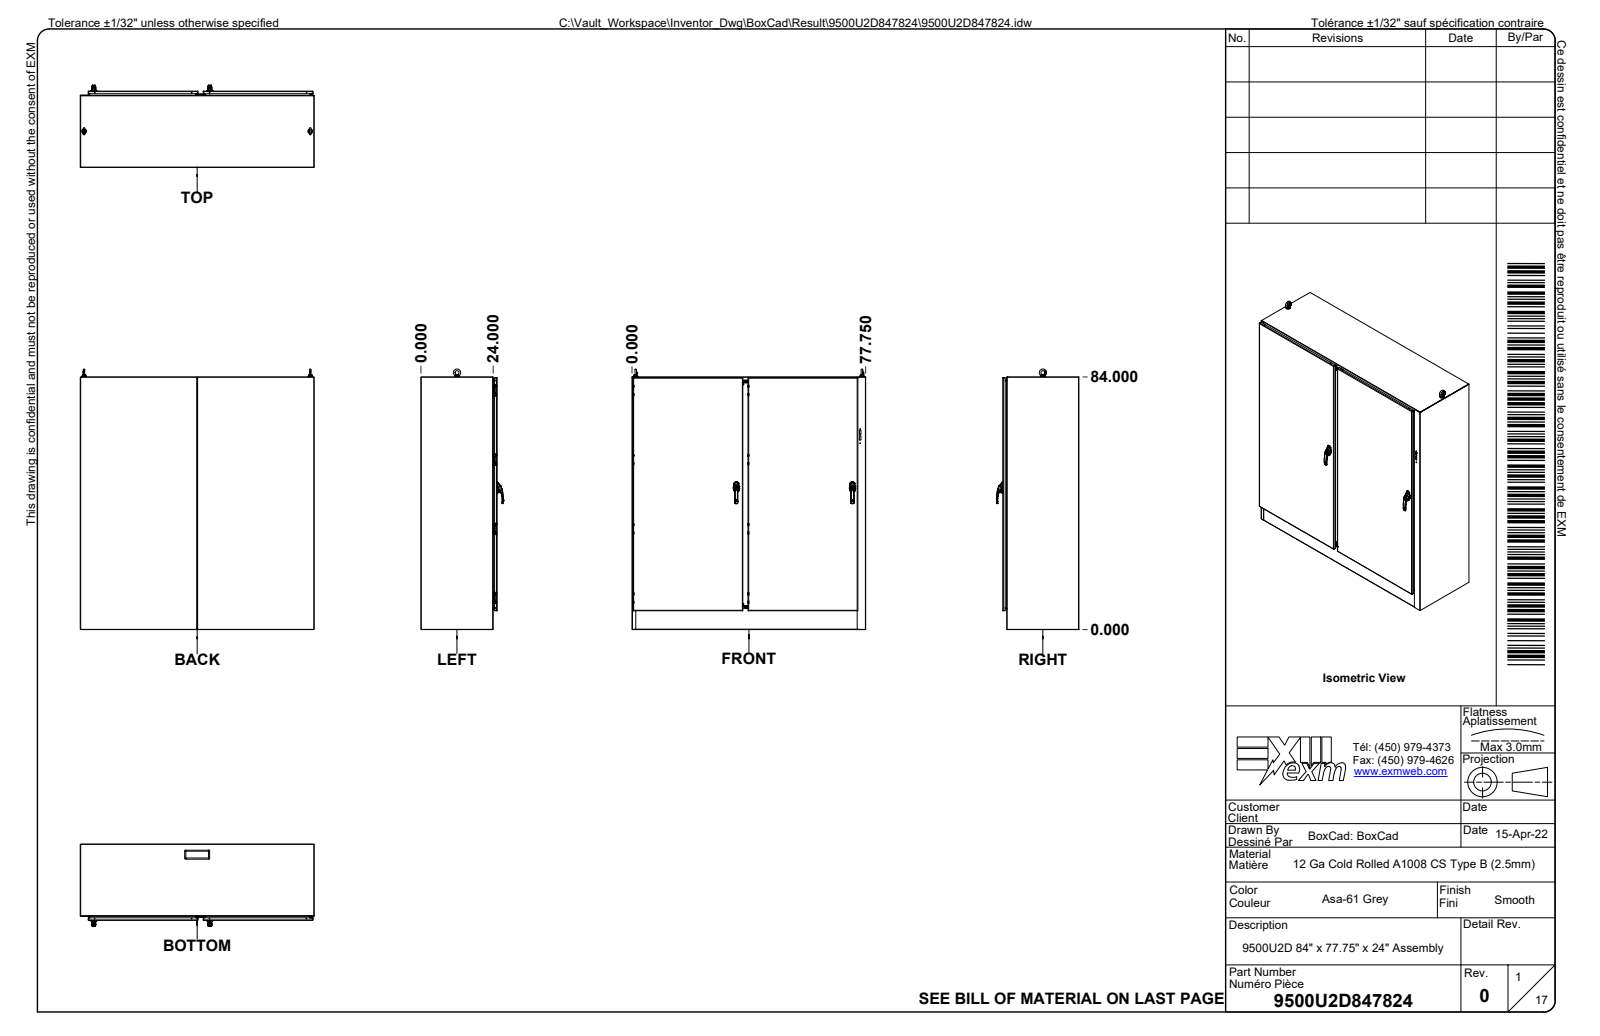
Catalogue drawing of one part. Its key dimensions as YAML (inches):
part_name: "9500U2D847824; 9500U2D847824B; 9500U2D847824BL-P; 9500U2D847824BR-P (+8 more)"
step_written_by: "Autodesk Inventor 2024 (AUTOMOTIVE_DESIGN)"
units: inches
bodies: {solids: 379, faces: 52831, planar: 18044, cylindrical: 13453, other: 21334}
overall_size: [86.638, 77.75, 27.422]
volume: 2651
surface_area: 60816
round_holes:
  - {diameter: 0.177, count: 404}
  - {diameter: 0.03, count: 50}
  - {diameter: 0.201, count: 37}
  - {diameter: 0.315, count: 30}
  - {diameter: 0.043, count: 16}
  - {diameter: 0.394, count: 14}
  - {diameter: 0.197, count: 13}
  - {diameter: 0.268, count: 13}
  - {diameter: 0.118, count: 12}
  - {diameter: 0.374, count: 12}
  - {diameter: 0.194, count: 10}
  - {diameter: 0.341, count: 10}
round_bosses_or_shafts:
  - {diameter: 0.249, count: 288}
  - {diameter: 0.232, count: 57}
  - {diameter: 0.03, count: 50}
  - {diameter: 0.039, count: 29}
  - {diameter: 0.177, count: 23}
  - {diameter: 0.289, count: 22}
  - {diameter: 0.236, count: 17}
  - {diameter: 0.374, count: 15}
partial_cylinders:
  - {radius: 0.02, count: 1321}
  - {radius: 0.039, count: 940}
  - {radius: 0.008, count: 422}
  - {radius: 0.079, count: 387}
  - {radius: 0.01, count: 370}
  - {radius: 0.031, count: 183}
  - {radius: 0.012, count: 180}
  - {radius: 0.004, count: 168}
face_to_face_distances: [0.089, 25.255, 0.963, 24.292, 25.166, 25.344, 0.874, 24.381, 1.052, 24.203]
hole_center_spacings: [23, 1, 22, 22.883, 24, 38.232, 46, 73.883]
